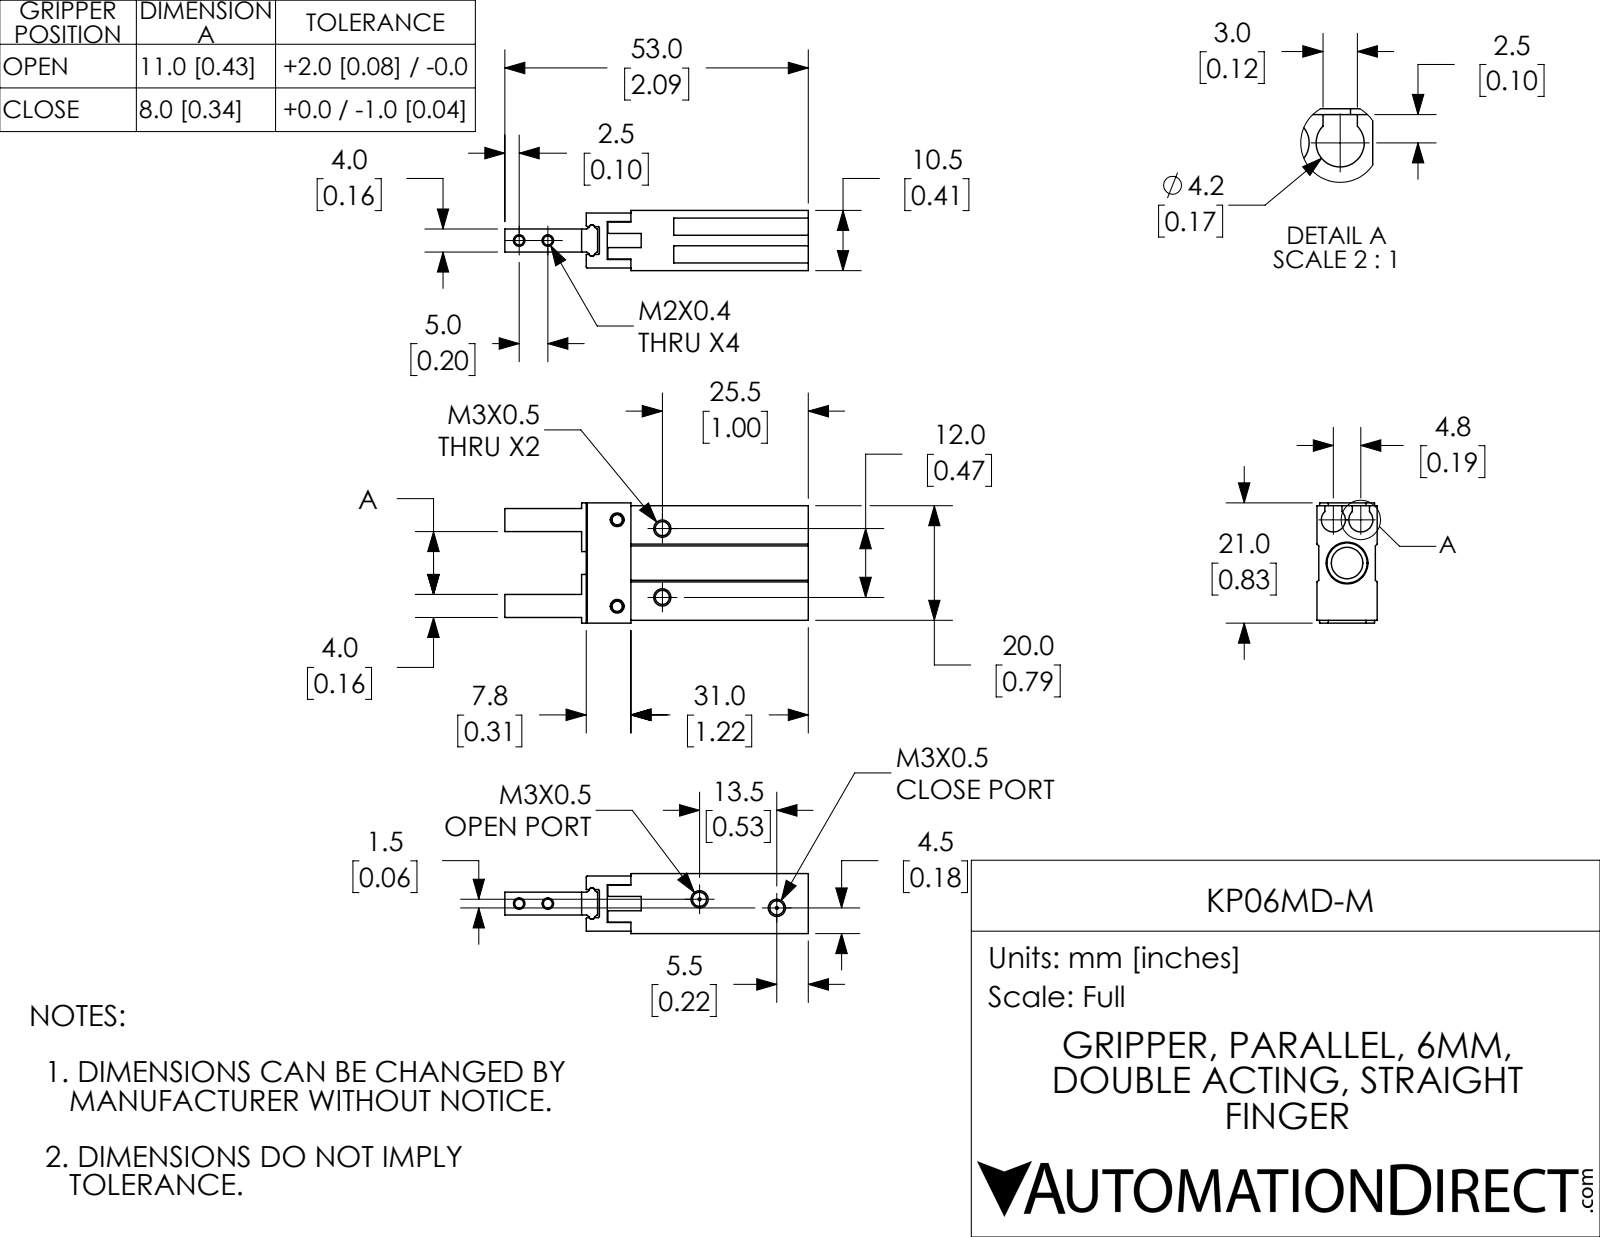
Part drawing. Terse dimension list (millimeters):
name: KP06MD-M; KP06MD-M-3; KP06MD-M-2; KP06MD-M-1
written by: SolidWorks 2017 (CONFIG_CONTROL_DESIGN)
unit: mm
bodies: 3 solids, 184 faces (94 planar, 44 cylindrical, 46 other)
size: 53 × 21 × 10.5
volume: 7 021 mm³; area: 5 178 mm²
holes: 3× ⌀2.46, 2× ⌀0.5, 2× ⌀1.57, 2× ⌀3.1, 1× ⌀2.46, 1× ⌀5.5, 1× ⌀7
rounds: 4× R0.2, 2× R0.5, 2× R2.1
face distances: 4, 3.25, 10.5, 2, 10.2, 3.7, 0.45, 2.8, 6.5, 10.05
hole spacings: 5, 12, 13.58, 26.51, 31.51, 40.01, 45.01
